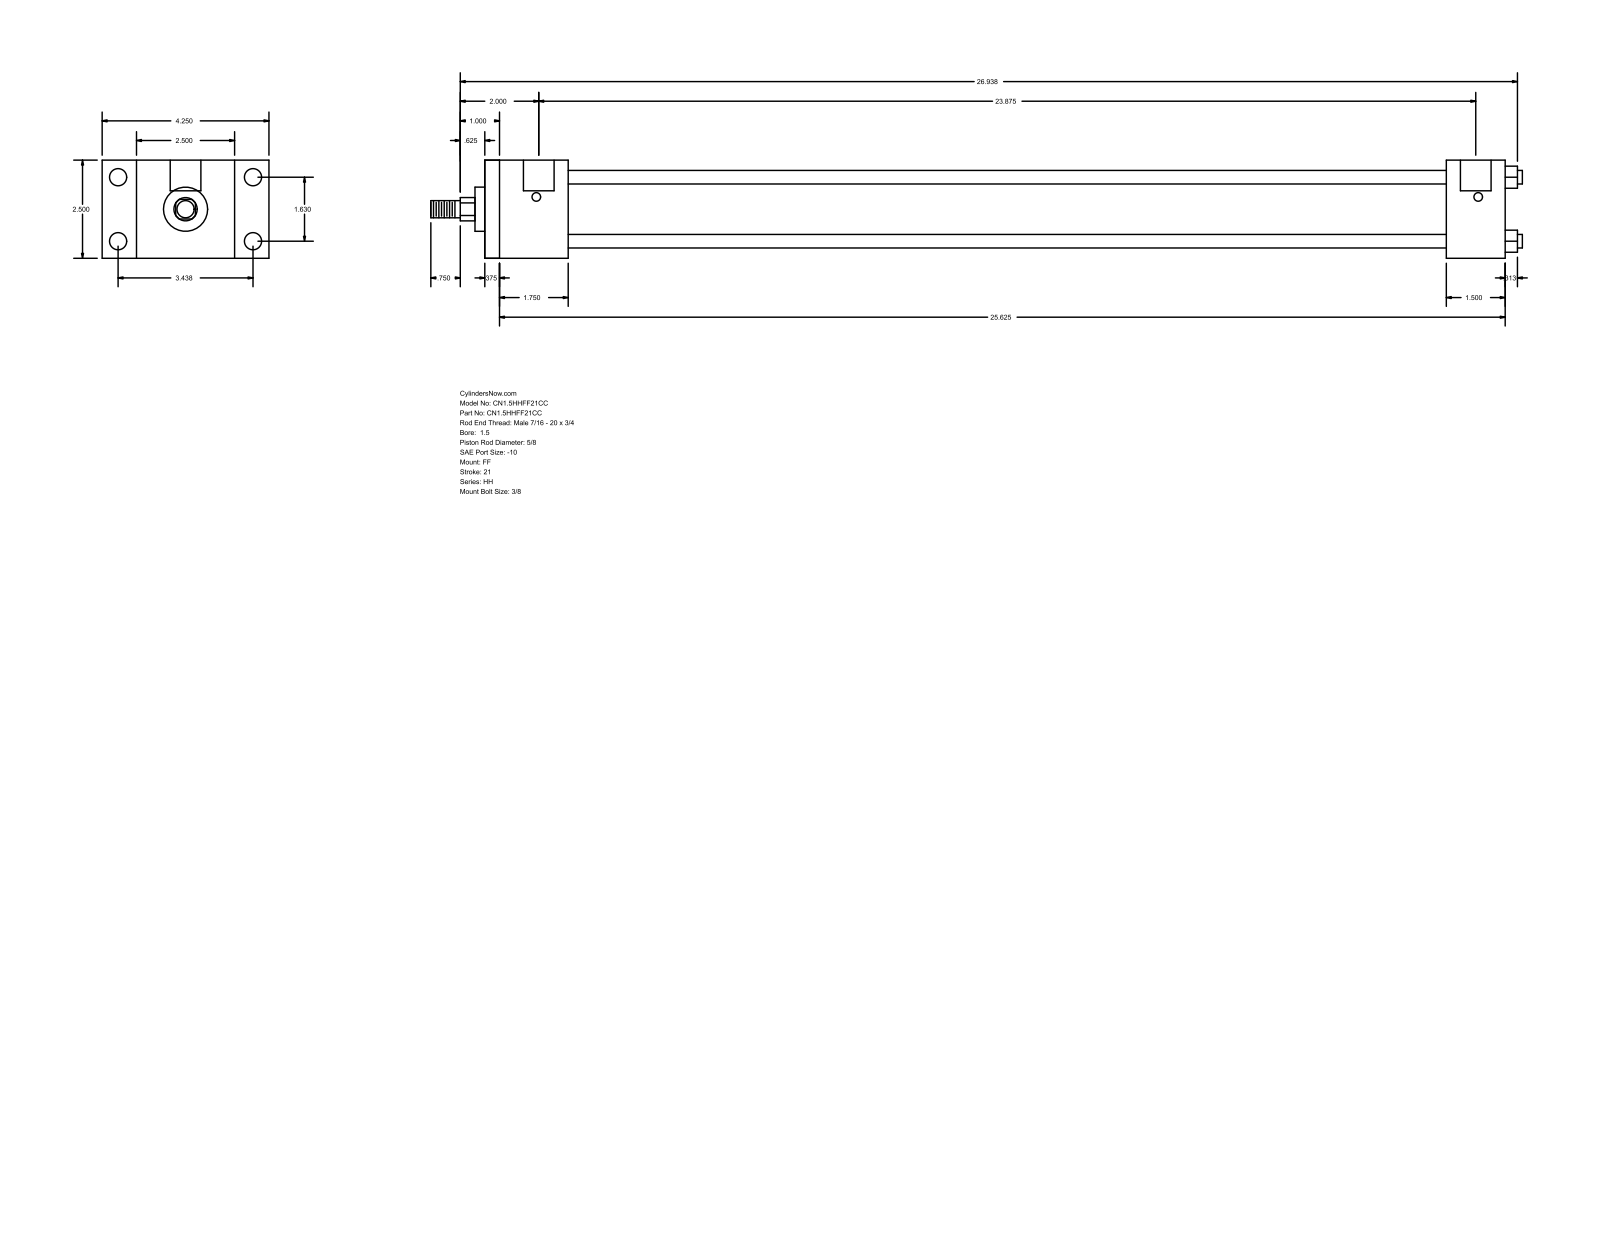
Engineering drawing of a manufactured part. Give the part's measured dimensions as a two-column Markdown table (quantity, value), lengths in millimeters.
| quantity | value |
| --- | --- |
| part name | HH_FF__0150_0.625 |
| STEP written by | GSSL Pune (CONFIG_CONTROL_DESIGN) |
| units | millimeters |
| bodies | 0 solids, 92 faces (64 planar, 28 cylindrical, 0 other) |
| overall size | 706.44 × 107.95 × 63.5 |
| round holes (diameter × count) | 5.56 × 4, 11.13 × 4, 19.84 × 2 |
| round bosses / shafts (diameter × count) | 8.76 × 4, 44.45 × 1, 28.57 × 1, 15.88 × 1, 11.11 × 1 |
| partial cylindrical surfaces (radius × count) | 7.54 × 1 |
| main face-to-face distances | 63.5, 660.39, 38.1, 9.52, 650.87, 44.45, 53.97, 606.42, 622.29, 612.77 |
| hole center spacings | 41.4, 87.32, 96.64, 609.6, 1.58, 1.59, 606.43, 608.01 |
